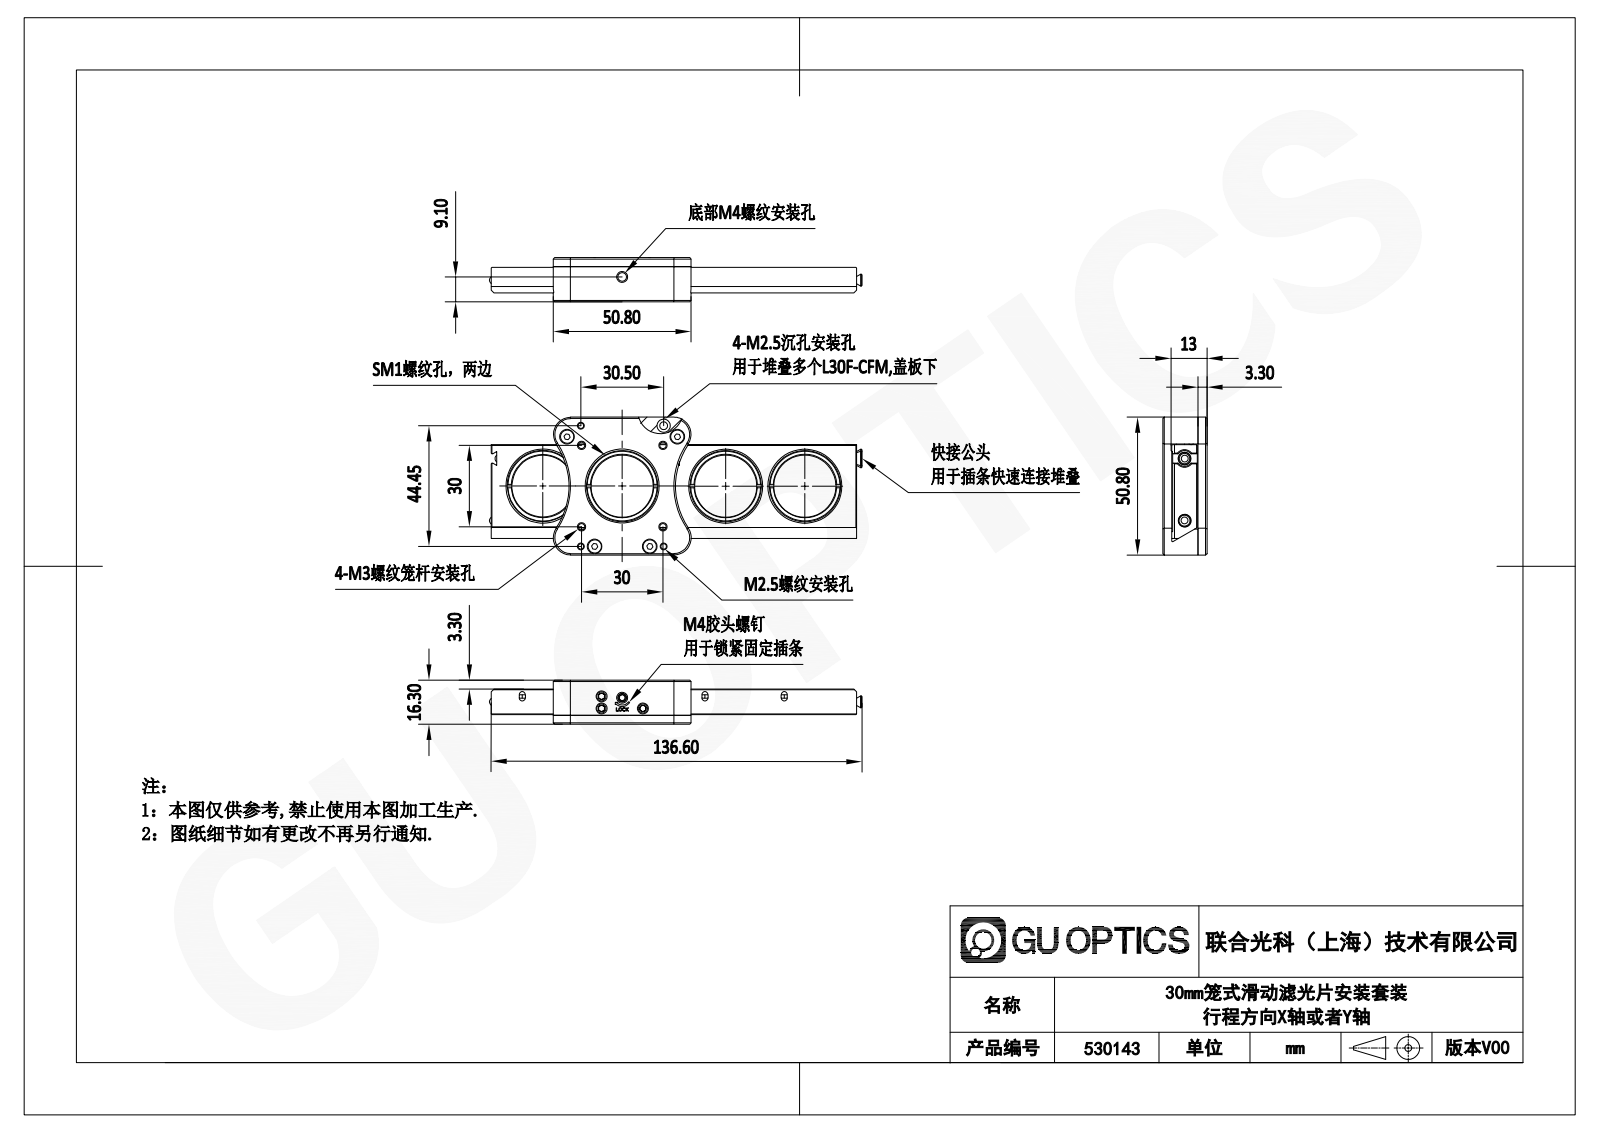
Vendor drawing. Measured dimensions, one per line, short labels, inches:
name: 530143
written by: SolidWorks 2020 (CONFIG_CONTROL_DESIGN)
unit: in
bodies: 21 solids, 619 faces (315 planar, 117 cylindrical, 187 other)
size: 5.403 × 2 × 0.64
volume: 2.444 in³; area: 44.04 in²
holes: 8× ⌀0.081, 8× ⌀0.114, 5× ⌀0.13, 4× ⌀0.098, 4× ⌀0.197, 4× ⌀0.902, 4× ⌀0.945, 3× ⌀0.12, 3× ⌀0.126, 2× ⌀0.157, 2× ⌀0.189, 2× ⌀1.035
bosses: 4× ⌀0.157, 4× ⌀0.098, 2× ⌀0.18, 2× ⌀0.157, 1× ⌀1.035, 1× ⌀0.118
rounds: 4× R0.037, 4× R0.25, 2× R1.083, 2× R1.313, 1× R0.01, 1× R0.11, 1× R0.118, 1× R0.13
face distances: 0.358, 0.368, 0.5, 0.142, 0.51, 0.14, 0.64, 0.498, 0.13, 0.38
hole spacings: 0.835, 1.181, 1.224, 1.888, 0.2, 0.244, 0.256, 0.284
